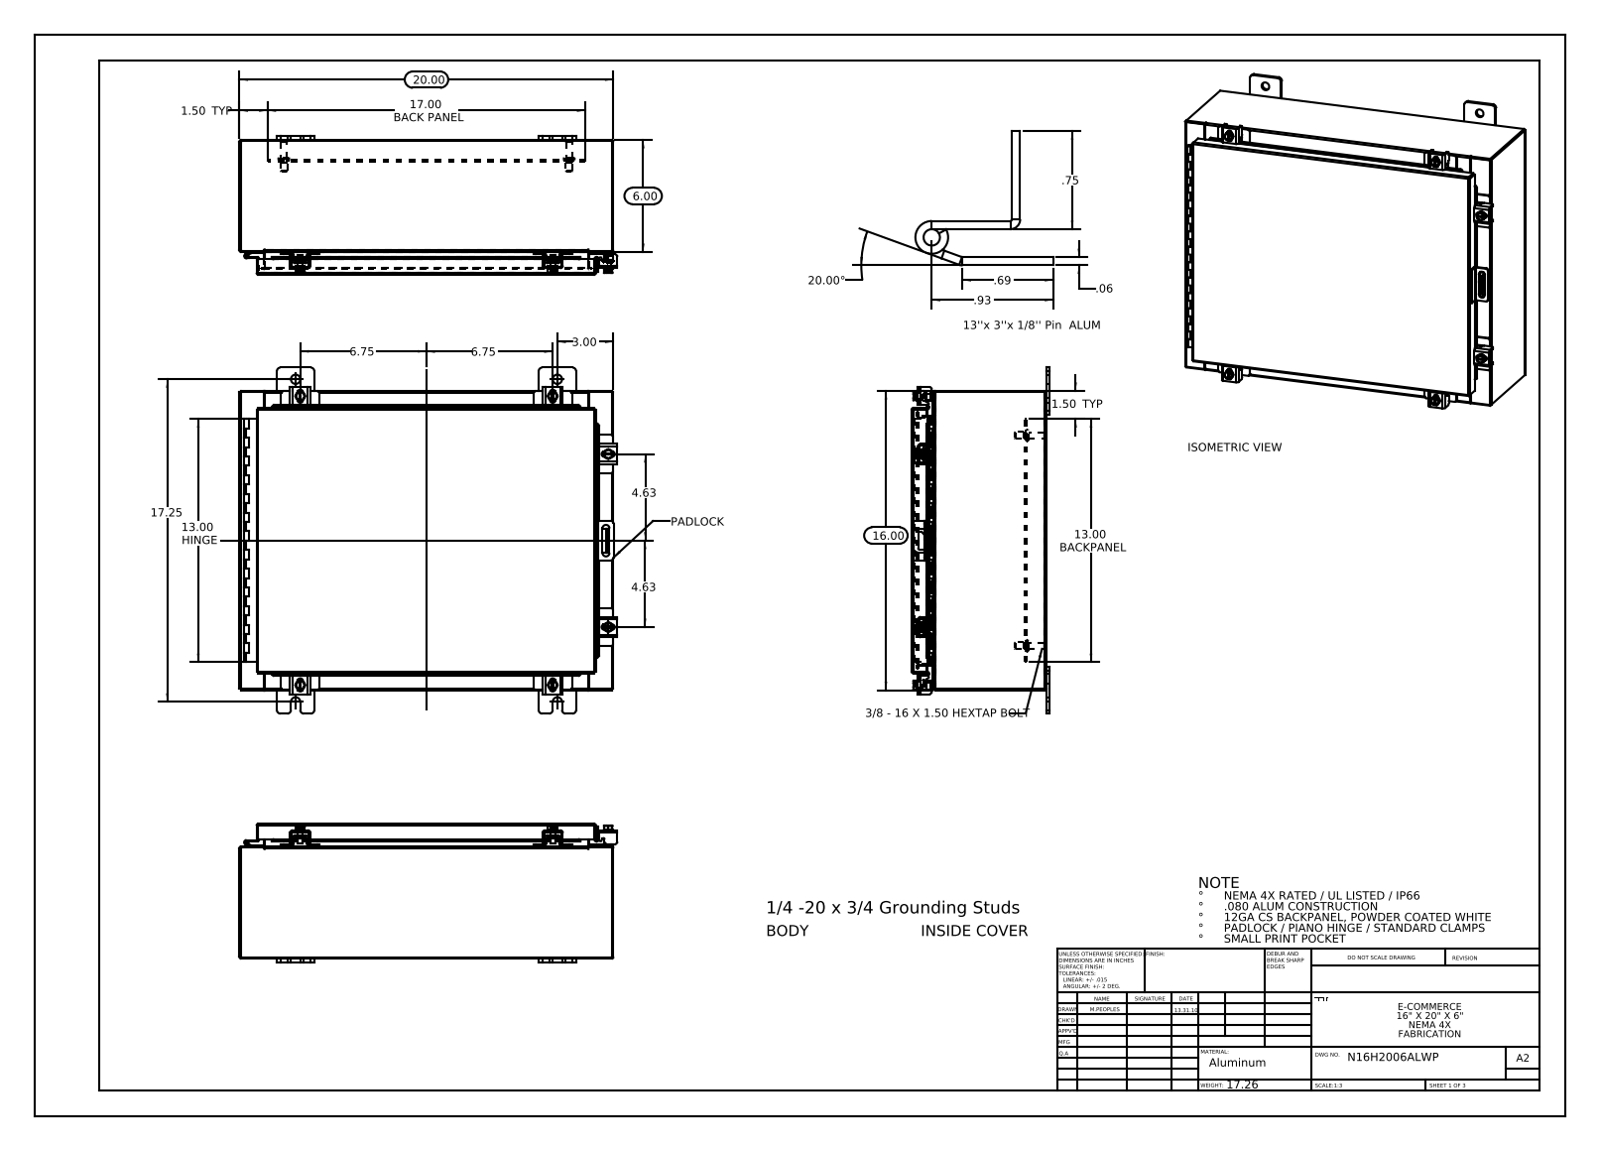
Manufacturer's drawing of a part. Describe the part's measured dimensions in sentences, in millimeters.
The part is named "N16H2006ALWP Bottom; N16H2006ALWP Backpanel; N16H2006ALWP 22104005_DEFAULT; N16H2006ALWP Standard Clamps (+8 more)". Its 3-D file was written by "SolidWorks 2013 (CONFIG_CONTROL_DESIGN)". It is 47 solids with 1501 faces: 800 planar, 605 cylindrical and 96 other. Overall it measures 513.4 by 469.9 by 187.7 millimeters. Its volume is 2 001 000 cubic millimeters and its surface area 1 991 000 square millimeters. Round holes: 8 of diameter 12.7, 6 of diameter 5.4, 6 of diameter 6.6, 2 of diameter 3.2, 1 of diameter 3.2. Round bosses or shafts: 7 of diameter 6.4, 6 of diameter 12.7, 6 of diameter 10.1, 4 of diameter 15.9, 4 of diameter 9.5, 4 of diameter 8.4. Partial cylindrical surfaces (rounded edges, fillets, slot ends): 30 of radius 1.5, 24 of radius 4.8, 23 of radius 0.3, 21 of radius 2.2, 12 of radius 3, 12 of radius 3.6, 10 of radius 3.2, 9 of radius 1.3. The main face-to-face distances are 1.9, 181, 182.9, 179.1, 404.5, 25.4, 27.3, 153.7, 155.6, 29.9. The hole center spacings are 339.9, 498.3, 10.9, 23.7, 47.2, 57.8, 57.8, 59.1.
